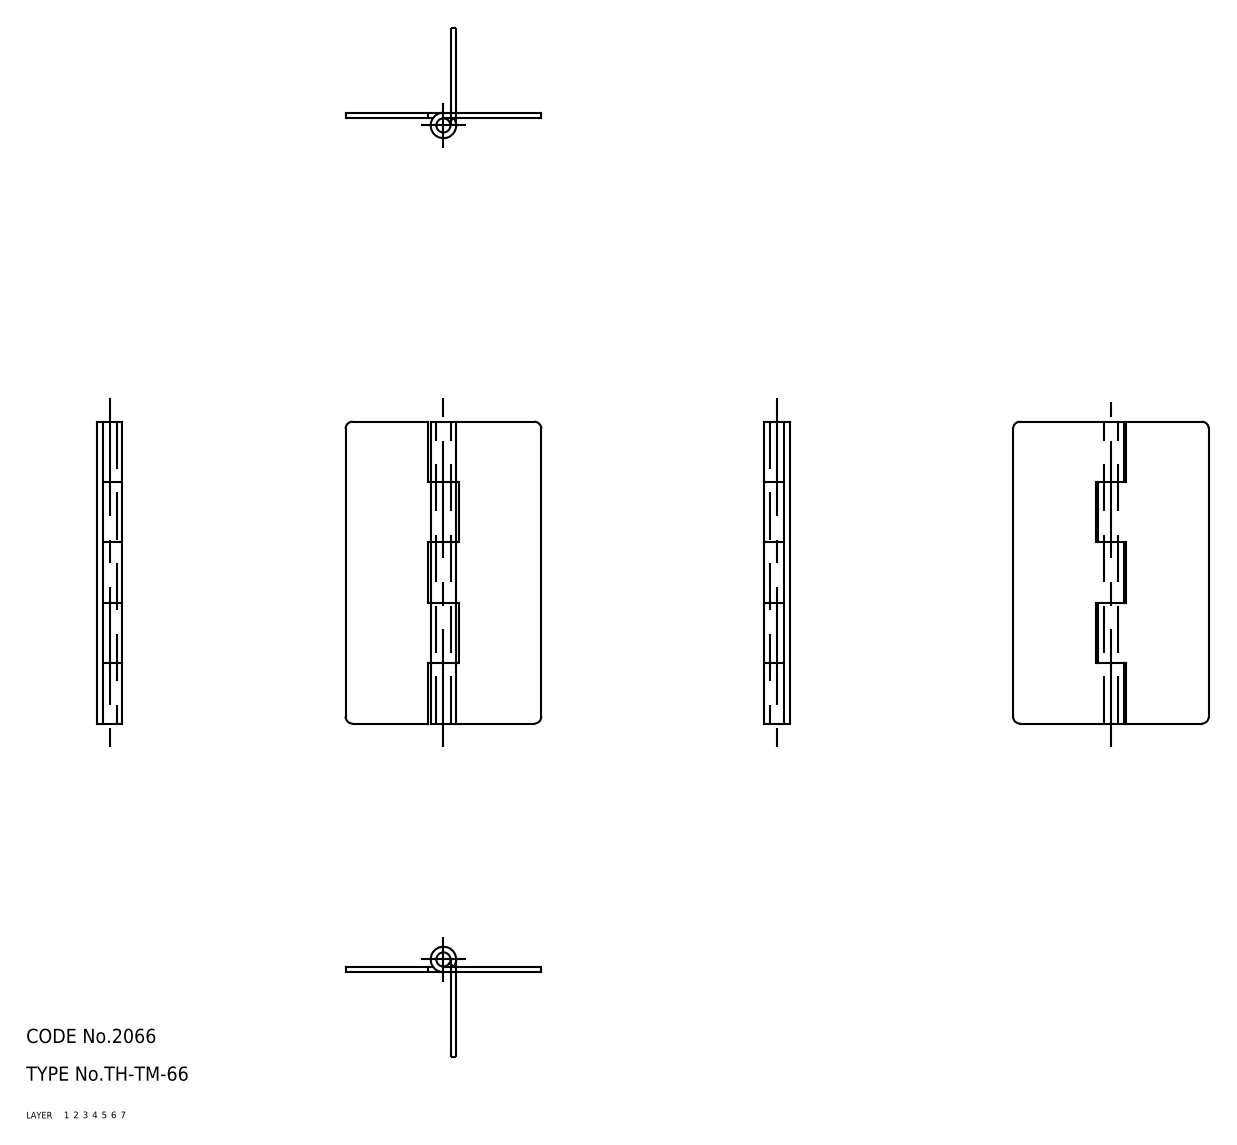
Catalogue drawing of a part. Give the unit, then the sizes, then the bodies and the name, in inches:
Units: inches
Overall size (bounding box): 2.52 × 1.634 × 0.213
Volume: 0.259 in³ · Surface area: 11.61 in²
Bodies: 3 solids, 46 faces (0 planar, 0 cylindrical, 46 other)
Part name (STEP PRODUCT): hinge piece_B; hinge piece_A; shaft; TH_TM_66_24835_36
STEP written by: CADfix (AUTOMOTIVE_DESIGN)
